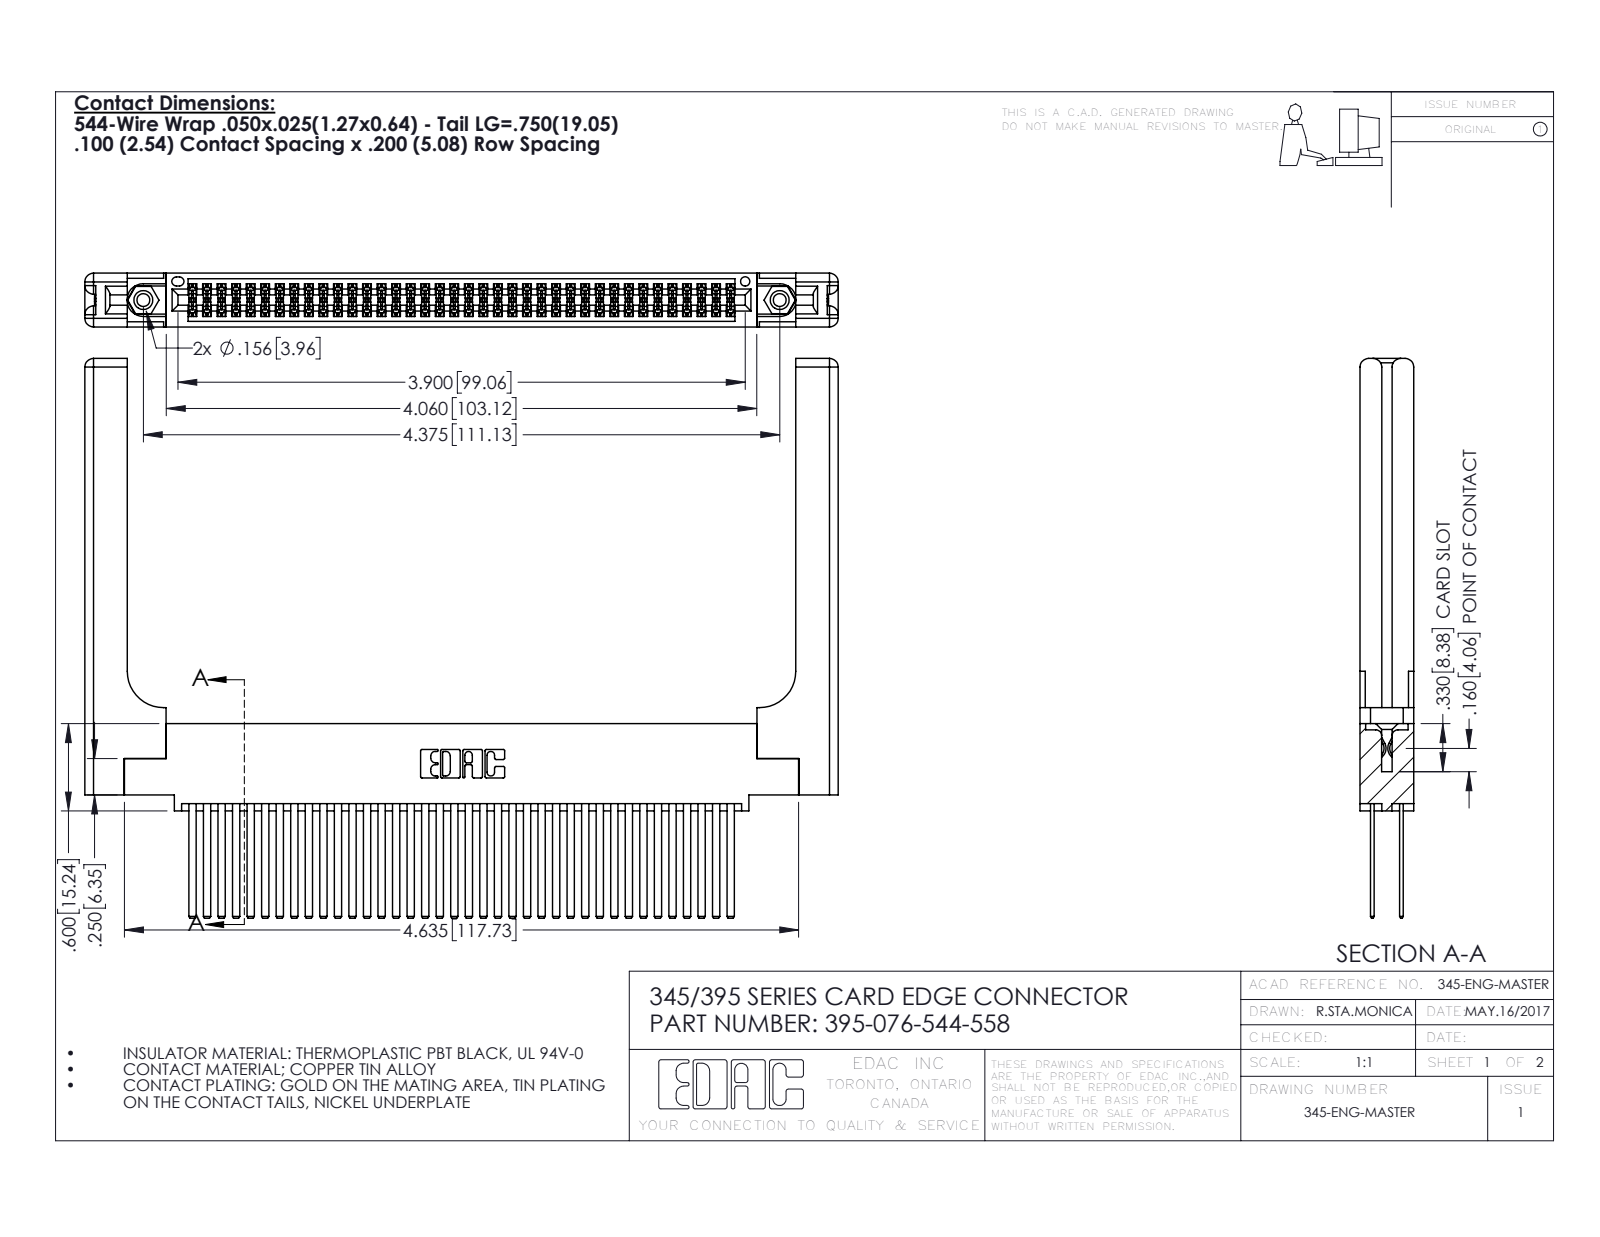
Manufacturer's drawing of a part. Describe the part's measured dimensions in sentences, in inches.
The part is named "345 Part_0.110 Offset - 0.156 Dia-TH; 345-250-001_345-250-001-102; 395-076-544-558; 345-292-001_345-293-144 (+1 more)". Its 3-D file was written by "SolidWorks 2016 (CONFIG_CONTROL_DESIGN)". It is 81 solids with 3730 faces: 2436 planar, 1234 cylindrical and 60 other. Overall it measures 5.179 by 3.847 by 0.37 inches. Its volume is 1.355 cubic inches and its surface area 44.17 square inches. Round holes: 2 of diameter 0.089, 2 of diameter 0.125, 2 of diameter 0.156, 1 of diameter 0.064. Round bosses or shafts: 2 of diameter 0.155. Partial cylindrical surfaces (rounded edges, fillets, slot ends): 114 of radius 0.006, 22 of radius 0.01, 16 of radius 0.06, 6 of radius 0.007, 6 of radius 0.031, 3 of radius 0.026, 2 of radius 0.014, 2 of radius 0.019. The main face-to-face distances are 0.072, 0.298, 0.098, 0.272, 0.025, 0.2, 0.37, 0.225, 0.175, 0.148. The hole center spacings are 0.27, 4.139, 4.375.
